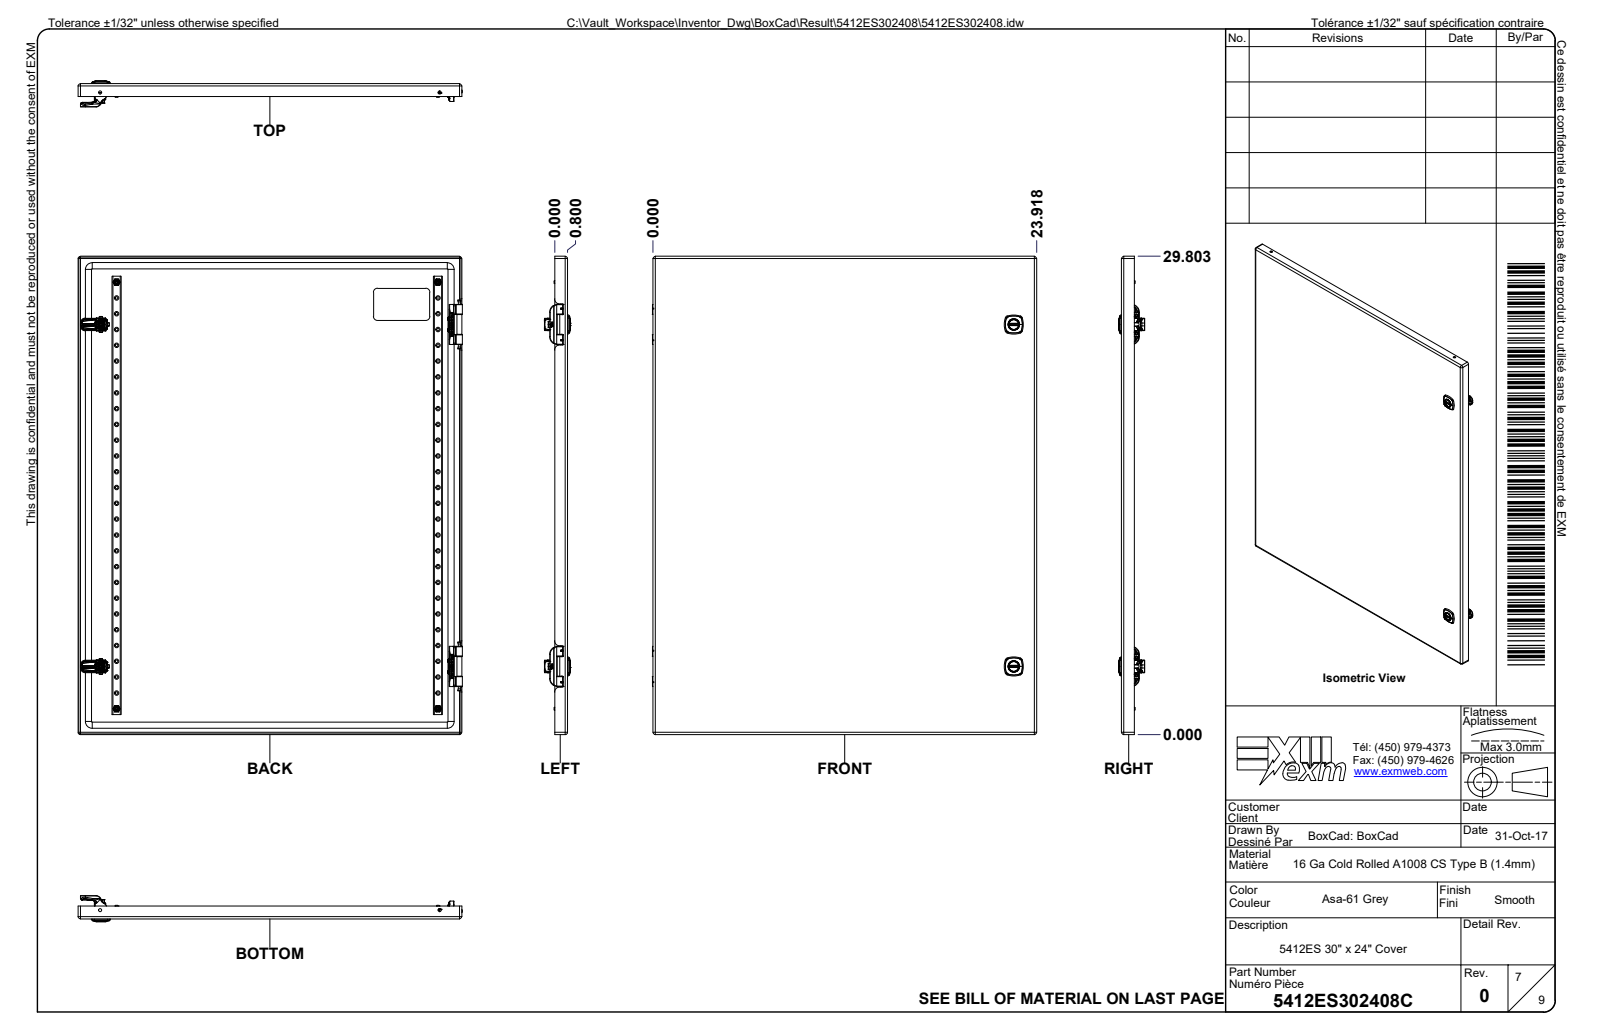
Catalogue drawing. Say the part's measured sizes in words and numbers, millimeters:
The part is named "5412ES302408; 5412ES302408B; 5412ES302408B-P; STK-Q-16005 (+8 more)". Its 3-D file was written by "Autodesk Inventor 2024 (AUTOMOTIVE_DESIGN)". It is 64 solids with 10126 faces: 3061 planar, 2575 cylindrical and 4490 other. Overall it measures 762 by 609.7 by 236.5 millimeters. Its volume is 3 600 000 cubic millimeters and its surface area 4 421 000 square millimeters. Round holes: 52 of diameter 4.2, 9 of diameter 0.8, 8 of diameter 1.1, 8 of diameter 5.1, 8 of diameter 8, 6 of diameter 7.9, 4 of diameter 4.5, 4 of diameter 5, 4 of diameter 6.8, 4 of diameter 6.9, 4 of diameter 7.4, 4 of diameter 9.9. Round bosses or shafts: 52 of diameter 6, 9 of diameter 5.9, 9 of diameter 0.8, 8 of diameter 1, 4 of diameter 18.2, 4 of diameter 9.5, 4 of diameter 7.9, 4 of diameter 6.7. Partial cylindrical surfaces (rounded edges, fillets, slot ends): 263 of radius 0.5, 139 of radius 0.3, 101 of radius 1, 94 of radius 0.2, 50 of radius 0.3, 32 of radius 0.8, 30 of radius 0.4, 24 of radius 2.1. The main face-to-face distances are 1.3, 230.7, 229.3, 232, 23.5, 22.2, 207.1, 208.5, 26.2, 24.9. The hole center spacings are 50, 25, 75, 100, 125, 150, 175, 541.1.
